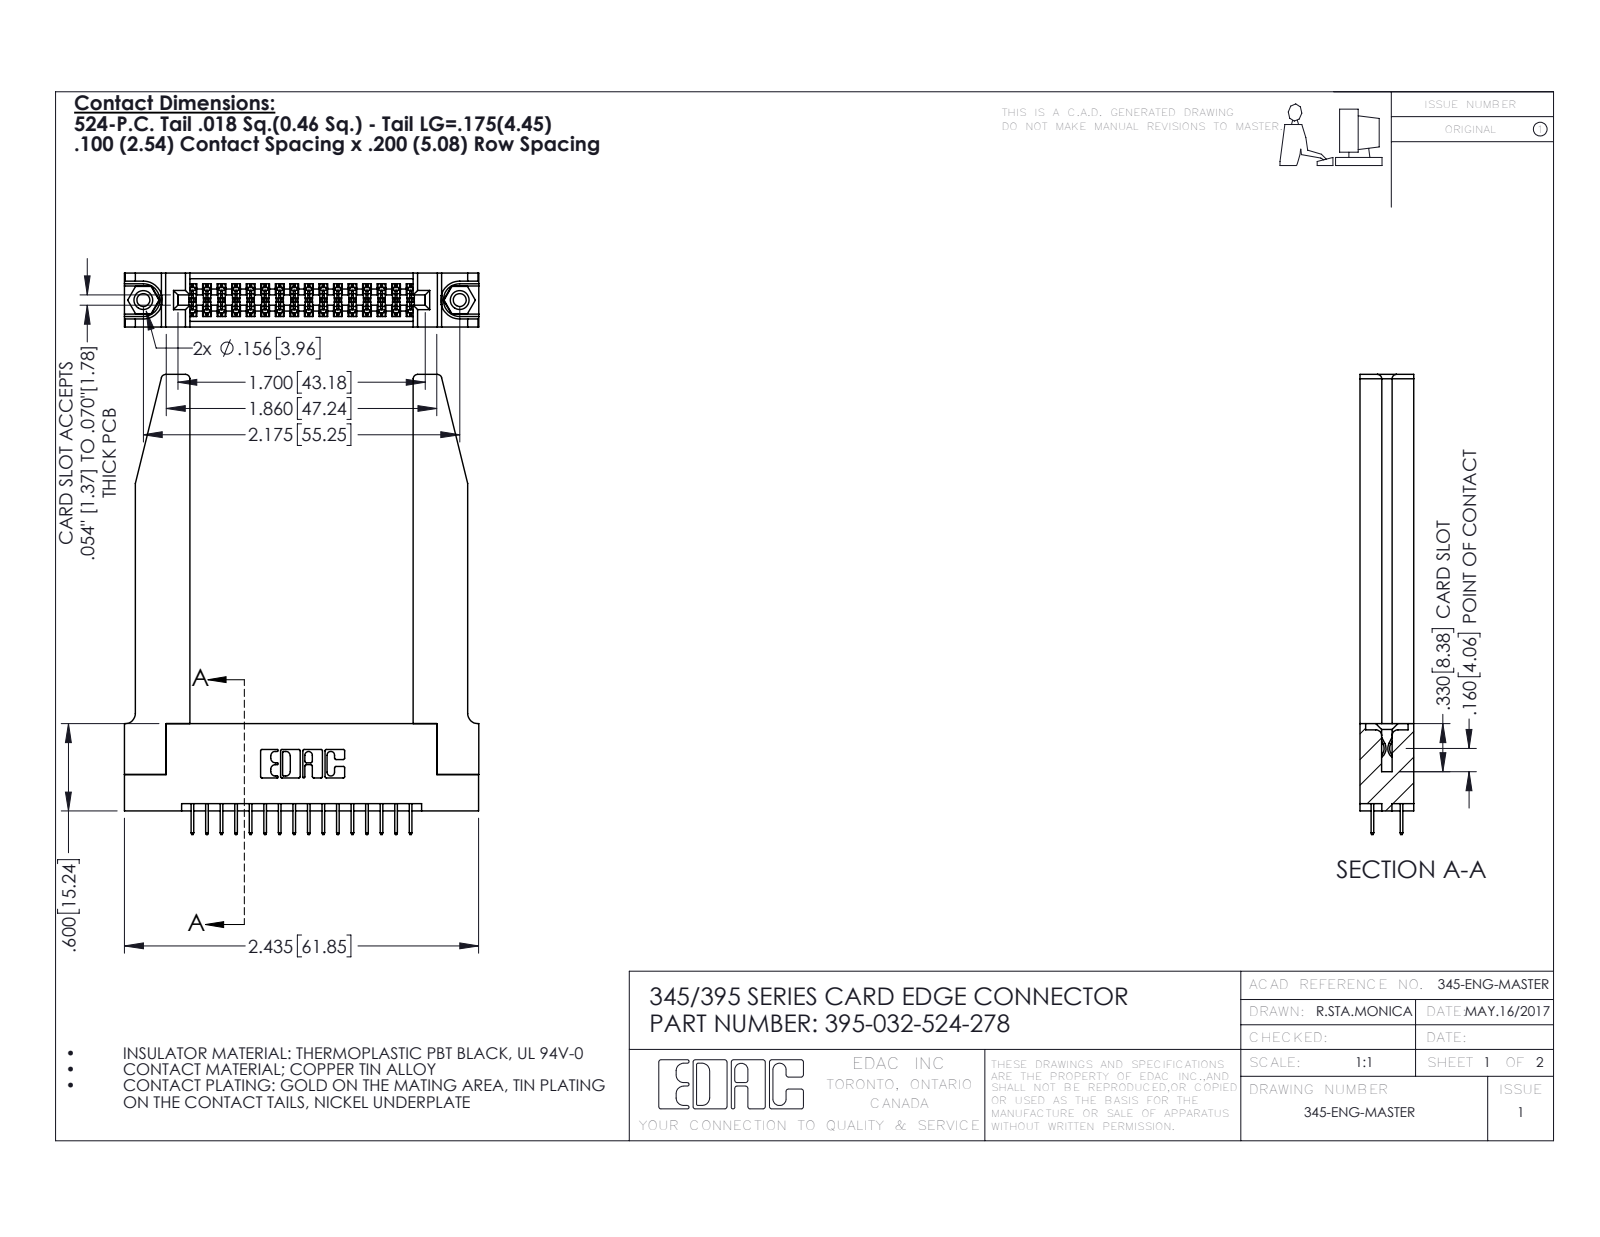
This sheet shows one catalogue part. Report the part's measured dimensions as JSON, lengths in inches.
{"part_name": "345-220-078_345-220-078; 395-032-524-278; 345-250-001_345-250-001-102; 345 Part_Flush Mounting Lugs - 0.156 Dia-TH (+1 more)", "step_written_by": "SolidWorks 2016 (CONFIG_CONTROL_DESIGN)", "units": "inches", "bodies": {"solids": 37, "faces": 2088, "planar": 1470, "cylindrical": 566, "other": 52}, "overall_size": [3.162, 2.436, 0.37], "volume_in3": 0.823, "surface_area_in2": 22.73, "round_holes": [[0.089, 2], [0.125, 2], [0.156, 2], [0.064, 1]], "round_bosses_or_shafts": [[0.155, 2]], "partial_cylinders_radius": [[0.006, 48], [0.01, 22], [0.03, 8], [0.007, 6], [0.031, 6], [0.026, 3], [0.014, 2], [0.019, 2]], "face_to_face_distances": [0.37, 0.072, 0.298, 0.2, 0.148, 0.15, 0.077, 0.22, 0.098, 0.272], "hole_center_spacings": [0.27, 1.942, 2.175]}
